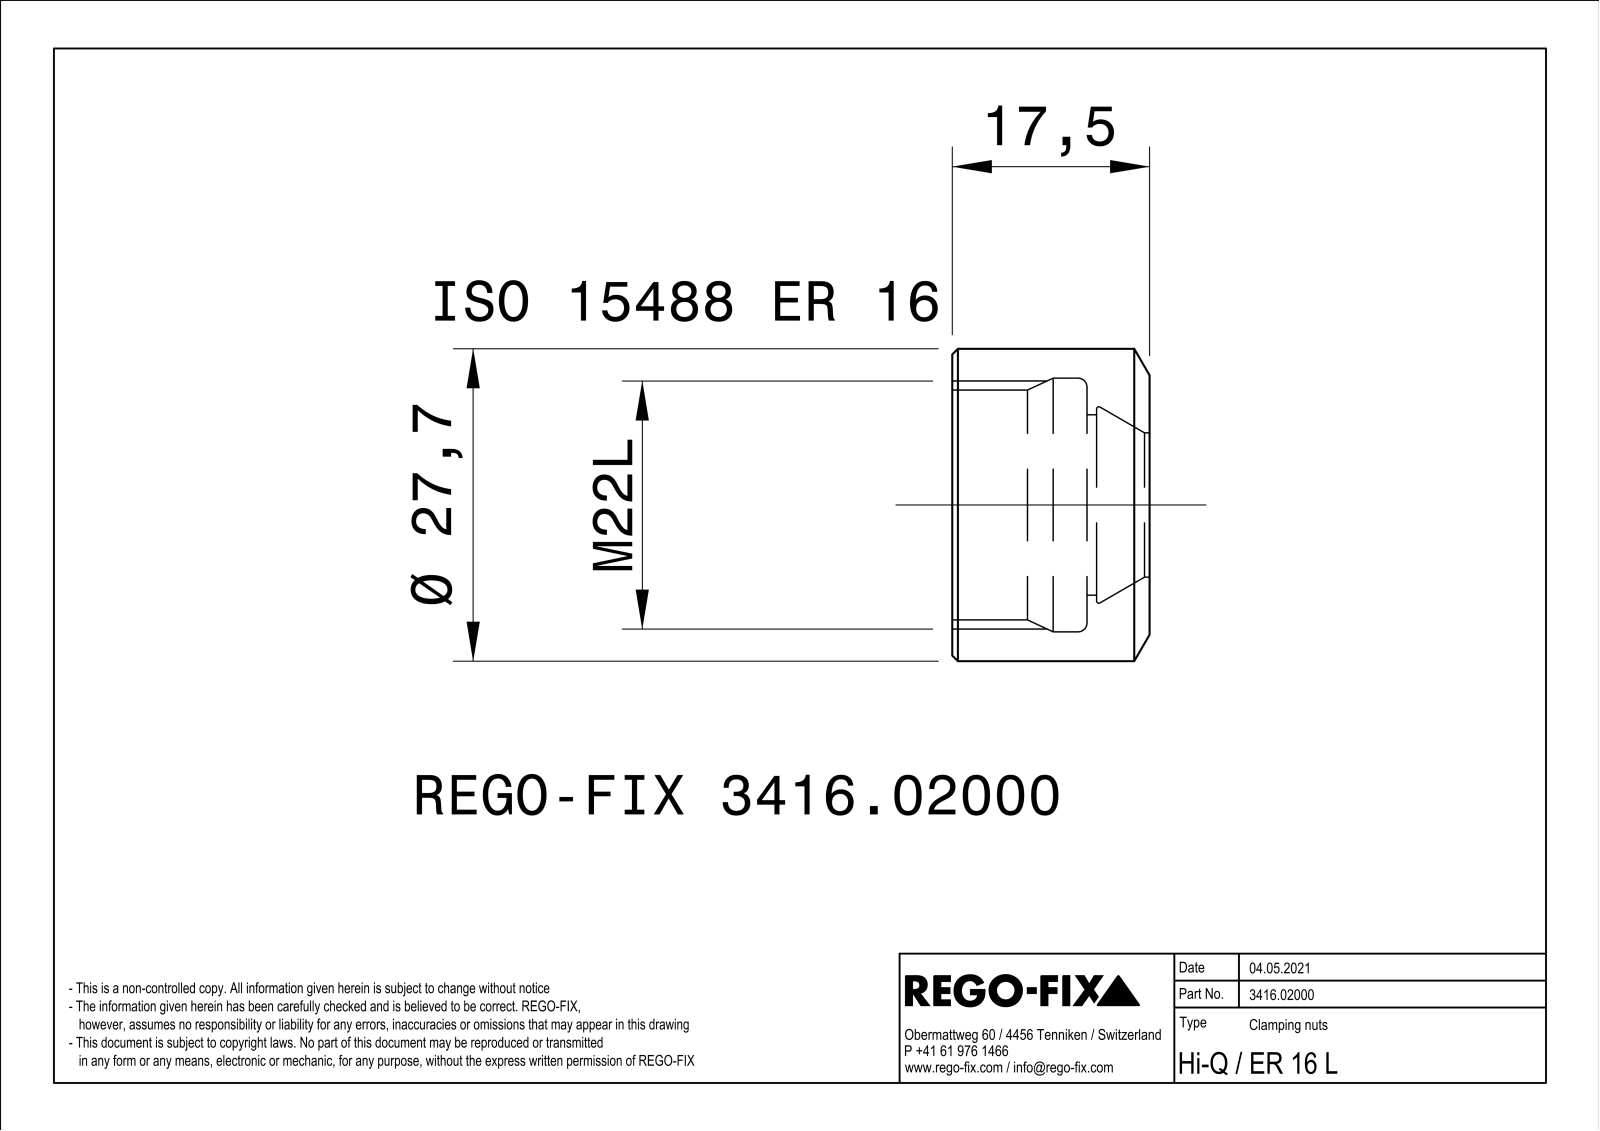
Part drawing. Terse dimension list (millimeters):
name: NOCUT
written by: SIEMENS PLM Software Solid Edge ST10 (AUTOMOTIVE_DESIGN)
unit: mm
bodies: 1 solid, 27 faces (16 planar, 5 cylindrical, 6 other)
size: 27.7 × 27.7 × 17.5
volume: 4 658 mm³; area: 3 434 mm²
holes: 1× ⌀12.8, 1× ⌀16, 1× ⌀20.38, 1× ⌀22.5
bosses: 1× ⌀27.7
face distances: 25, 17.5, 5.55, 11.95, 4.7, 0.85, 12.8
